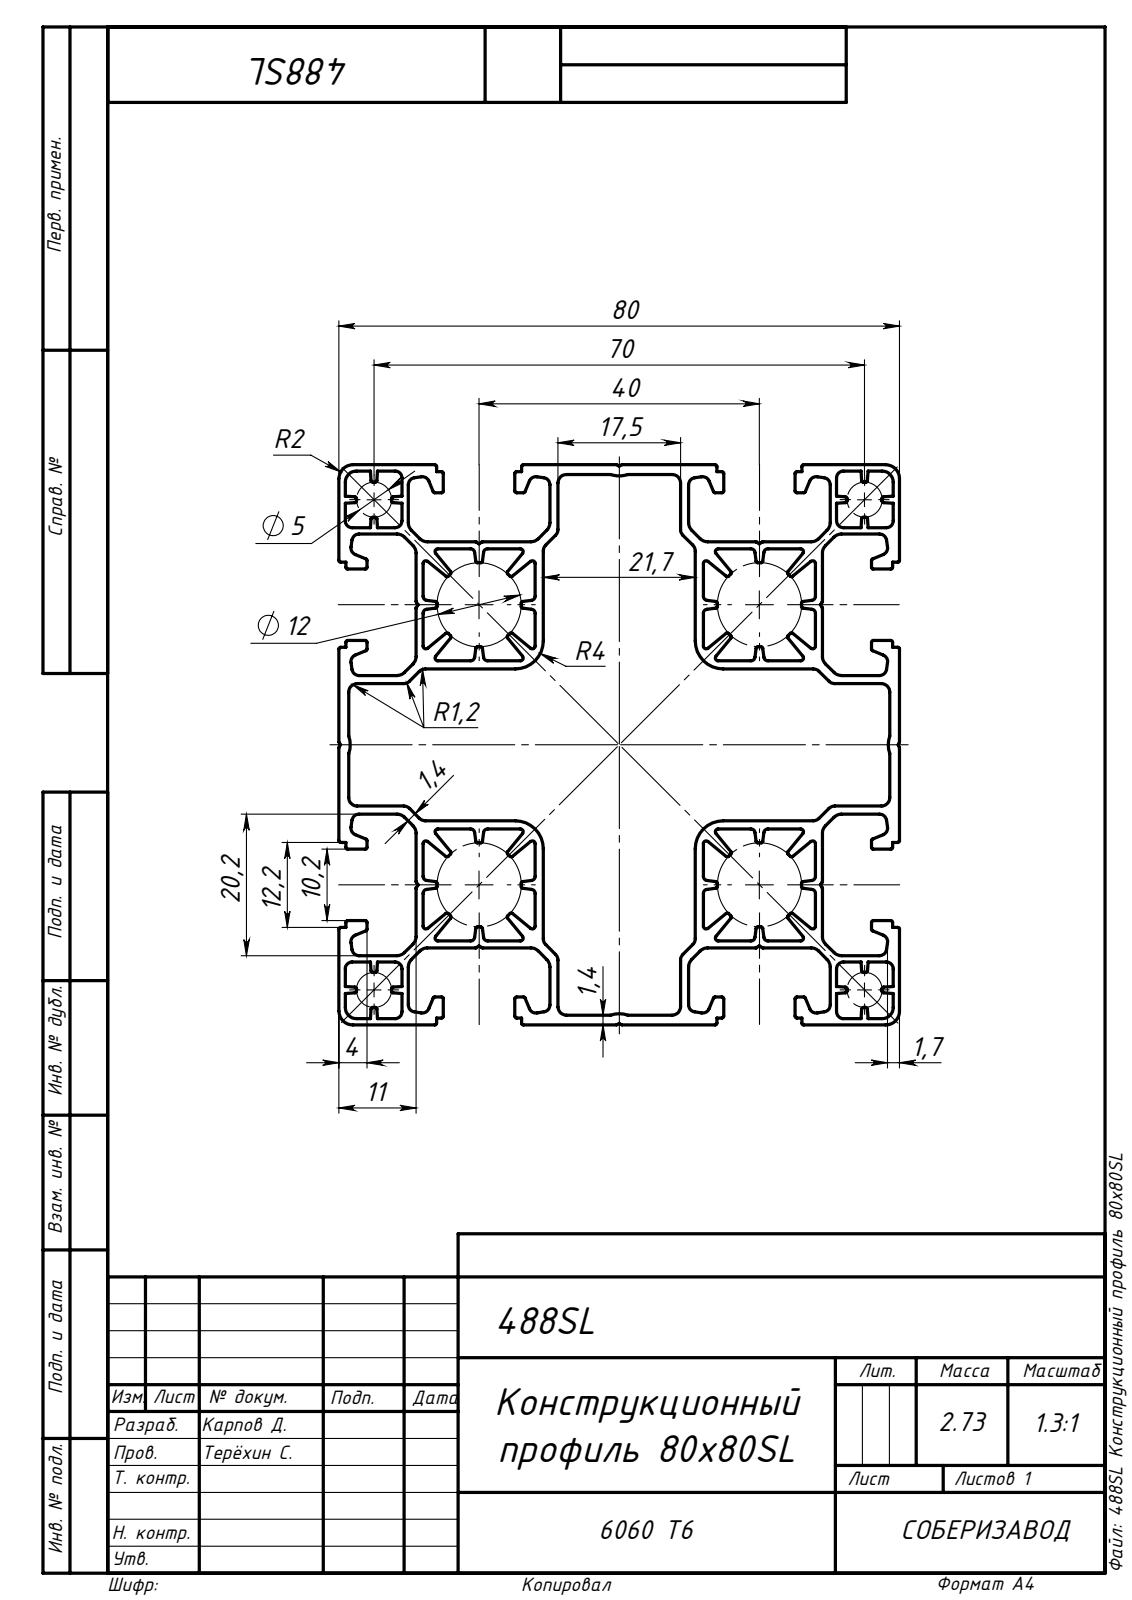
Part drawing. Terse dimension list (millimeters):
written by: SolidWorks 2018 (AUTOMOTIVE_DESIGN)
unit: mm
bodies: 1 solid, 846 faces (426 planar, 420 cylindrical, 0 other)
size: 1000 × 80 × 80
volume: 1 013 000 mm³; area: 1 523 000 mm²
rounds: 176× R0.25, 44× R1, 32× R0.4, 32× R0.6, 32× R1.5, 24× R1.2, 8× R4, 4× R1.6
face distances: 2.1, 1.16, 38.84, 40, 11, 69, 29.16, 50.84, 18.16, 39.84
